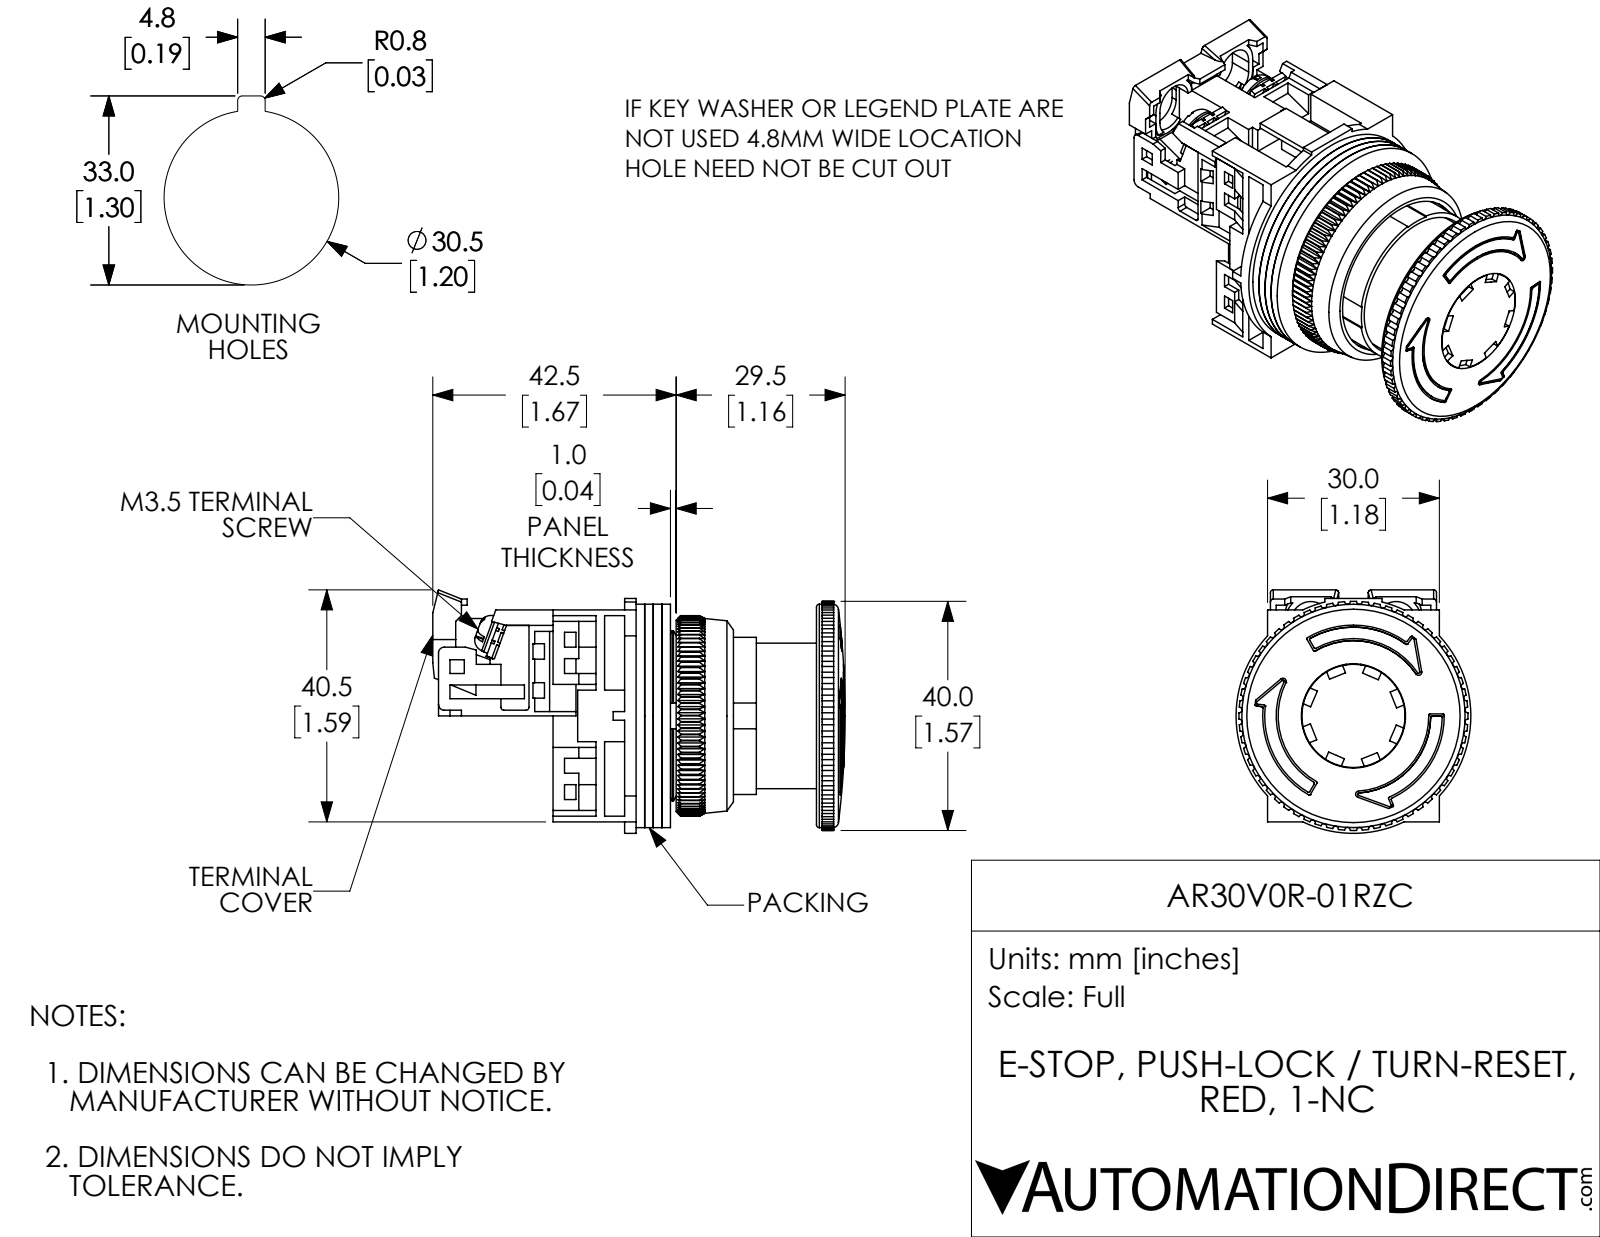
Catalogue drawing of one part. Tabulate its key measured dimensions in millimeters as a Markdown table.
| quantity | value |
| --- | --- |
| part name | AR30V0R-01RZC |
| STEP written by | SolidWorks 2017 (AUTOMOTIVE_DESIGN) |
| units | millimeters |
| bodies | 17 solids, 1626 faces (933 planar, 482 cylindrical, 211 other) |
| overall size | 72 × 42.5 × 41 |
| volume | 36 330 mm³ |
| surface area | 40 230 mm² |
| round holes (diameter × count) | 3.5 × 2, 3.6 × 2, 3 × 1, 13.8 × 1, 16 × 1, 18 × 1, 18.2 × 1, 20.4 × 1, 23.4 × 1, 26 × 1, 28.5 × 1, 29.8 × 1 |
| round bosses / shafts (diameter × count) | 6.6 × 2, 3.5 × 2, 39 × 1, 30 × 1, 25.4 × 1 |
| partial cylindrical surfaces (radius × count) | 0.5 × 66, 0.2 × 24, 1.5 × 8, 0.6 × 6, 1 × 2, 3.5 × 2, 4.5 × 2, 3 × 1 |
| main face-to-face distances | 1.5, 3, 4.5, 1, 3.5, 17.5, 5, 2, 8, 18.5 |
| hole center spacings | 14.7, 15.5 |
